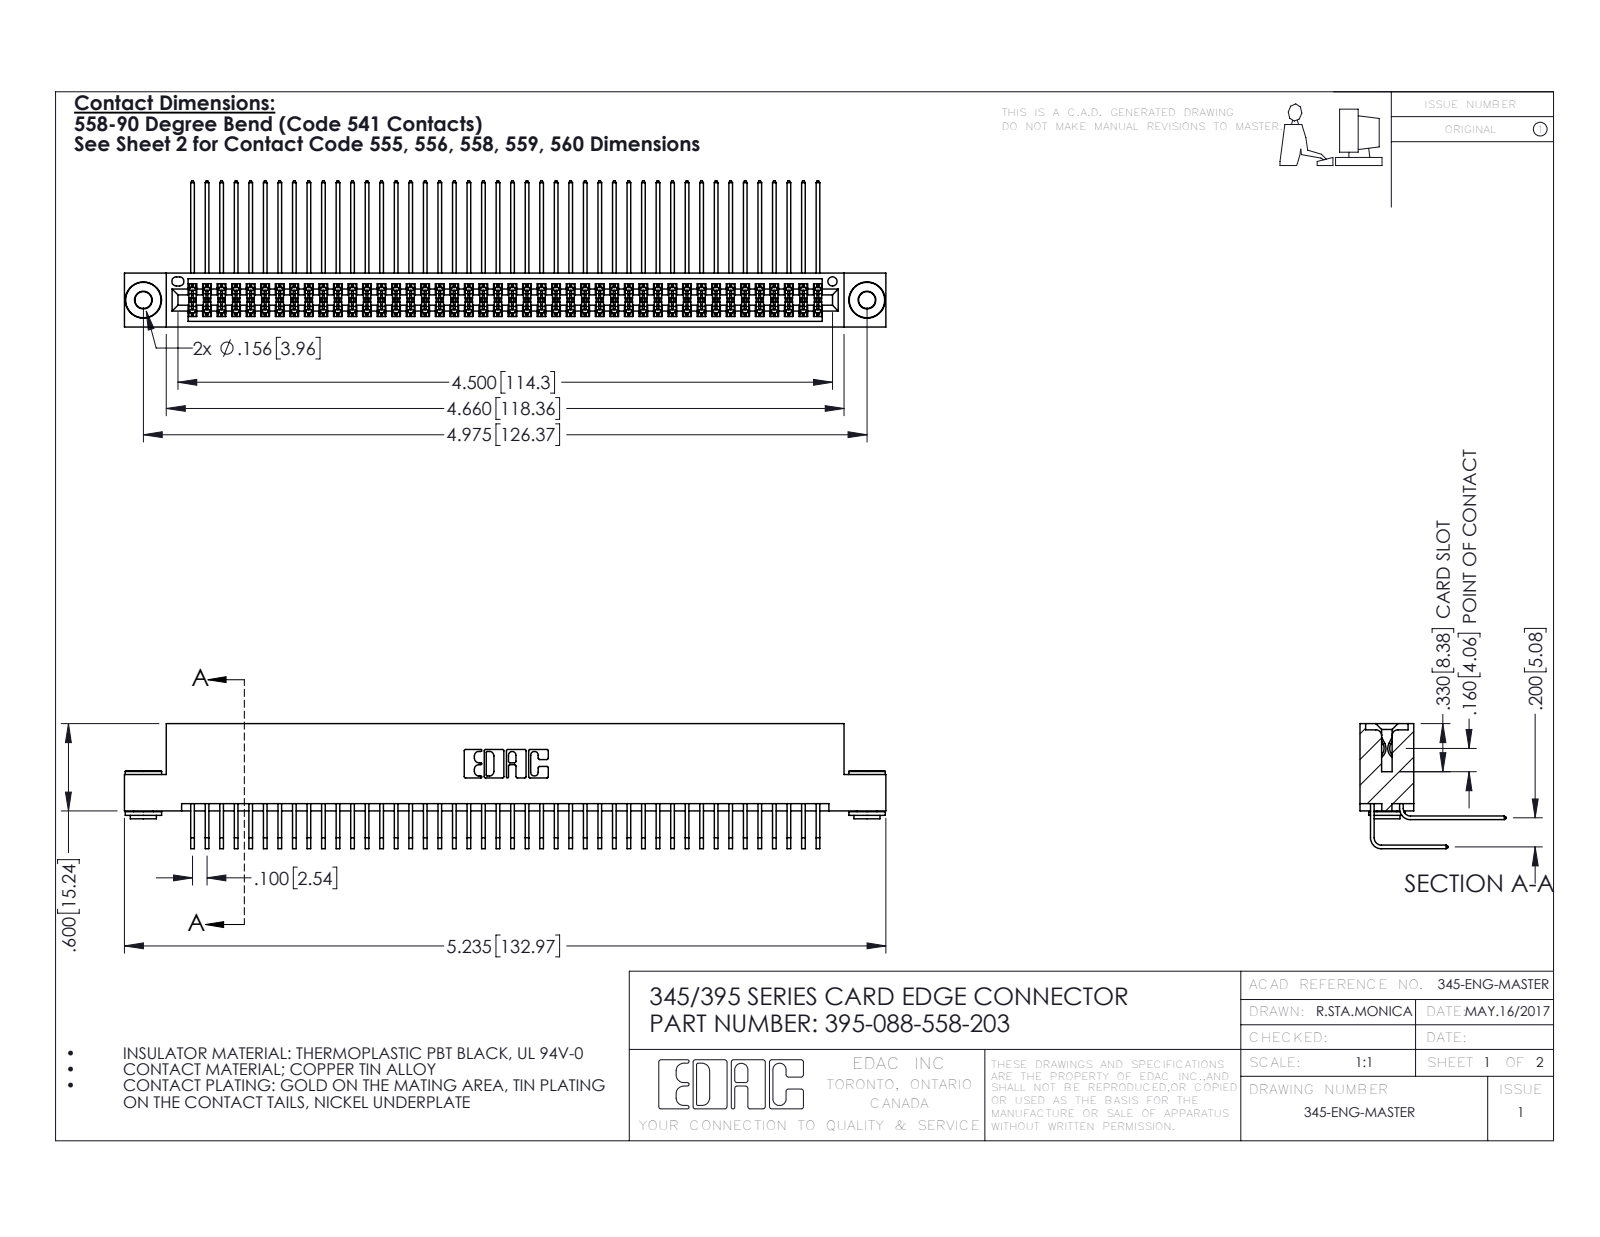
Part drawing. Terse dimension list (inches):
name: 345 Part_Flush Mounting Lugs - 0.156 Dia-TH; 345-250-002_345-250-002-102; 345-292-001_558 559 Tail - 1; 345-292-001_558 Tail - 2 (+1 more)
written by: SolidWorks 2016 (CONFIG_CONTROL_DESIGN)
unit: in
bodies: 91 solids, 4740 faces (3170 planar, 1562 cylindrical, 8 other)
size: 5.235 × 1.005 × 0.859
volume: 0.822 in³; area: 34.92 in²
holes: 2× ⌀0.116, 2× ⌀0.156, 1× ⌀0.064
bosses: 2× ⌀0.25, 2× ⌀0.18, 2× ⌀0.136
rounds: 133× R0.006, 22× R0.01, 6× R0.007, 6× R0.031, 3× R0.026, 2× R0.014, 2× R0.019, 2× R0.022
face distances: 0.072, 0.298, 0.2, 0.37, 0.025, 0.098, 0.272, 0.225, 0.025, 0.285
hole spacings: 0.27, 4.739, 4.975
